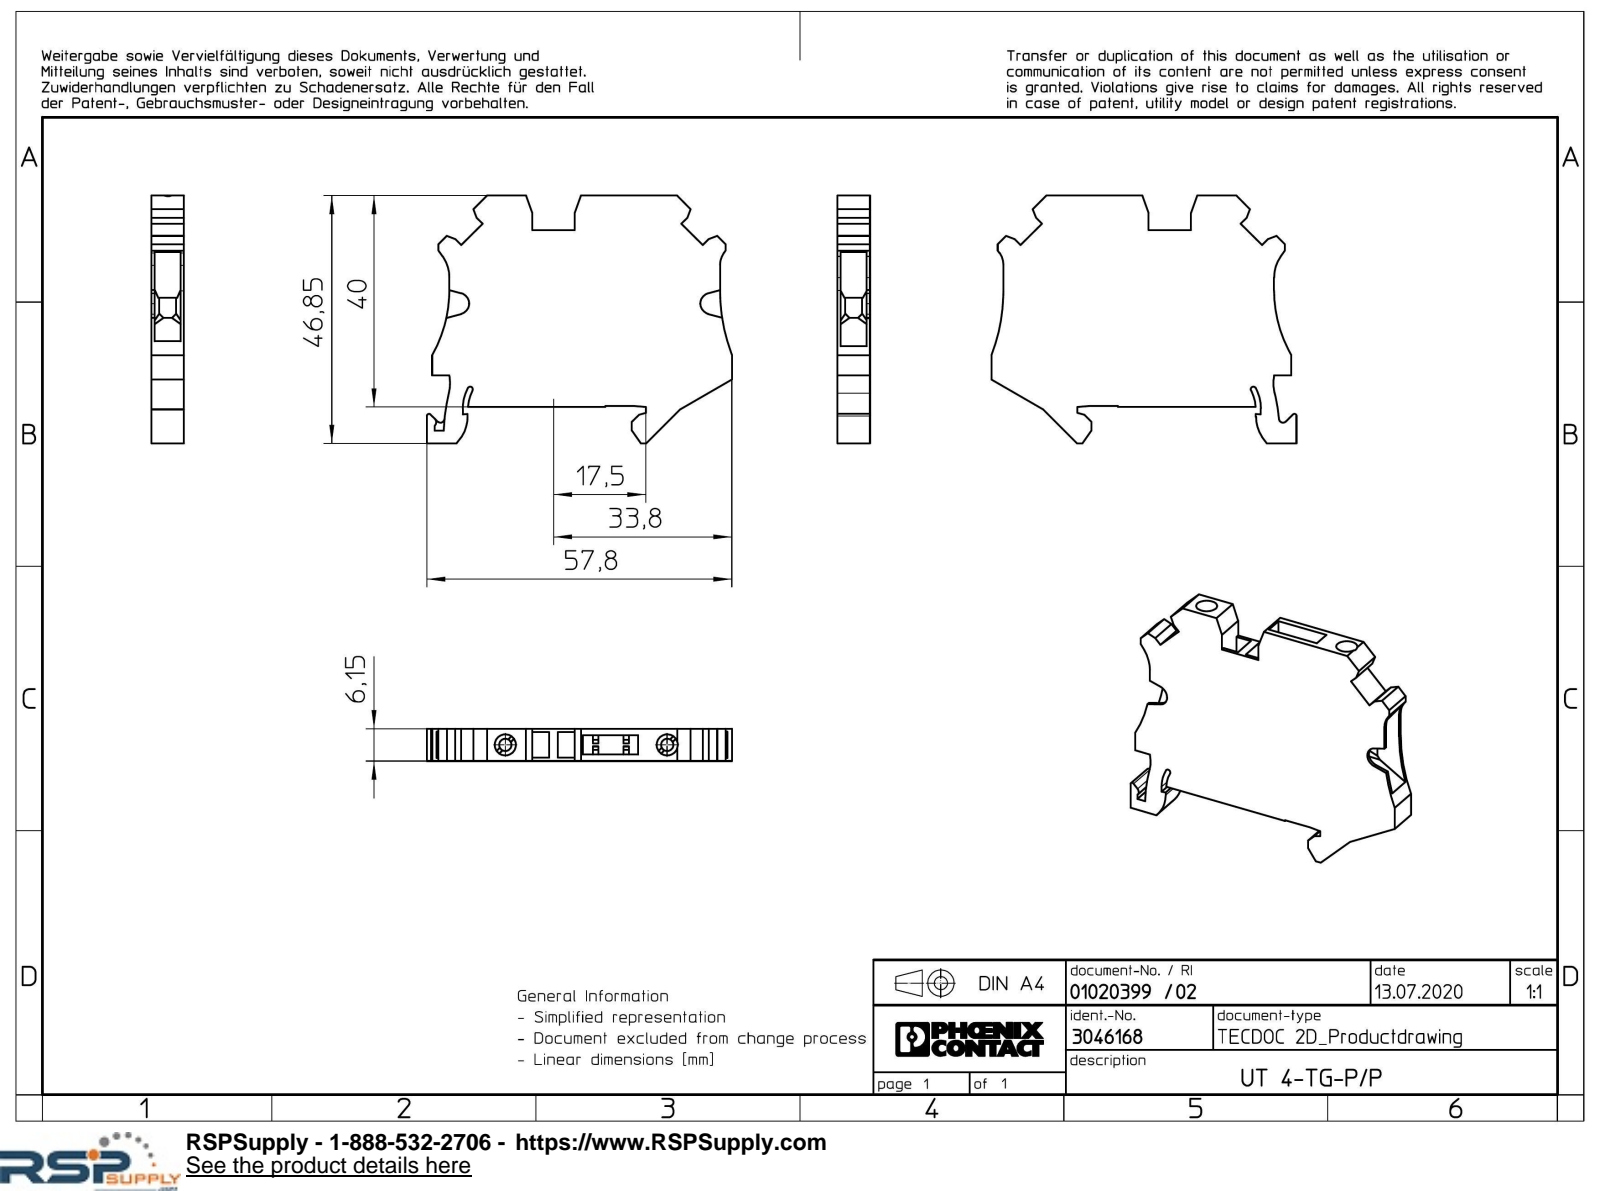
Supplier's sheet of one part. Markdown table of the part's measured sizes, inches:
| quantity | value |
| --- | --- |
| part name | UT_4-TG-P_P-select |
| STEP written by | Creo Elements/Direct Modeling 20.1A 29-Sep-2018 (C) Parametric Technology GmbH (AUTOMOTIVE_DESIGN) |
| units | inches |
| bodies | 1 solid, 190 faces (154 planar, 32 cylindrical, 4 other) |
| overall size | 2.276 × 1.844 × 0.242 |
| volume | 0.653 in³ |
| surface area | 10.62 in² |
| round holes (diameter × count) | 0.093 × 2, 0.157 × 2 |
| partial cylindrical surfaces (radius × count) | 0.079 × 4, 0.01 × 2, 0.276 × 2, 0.016 × 1, 0.02 × 1, 0.03 × 1, 0.035 × 1, 0.157 × 1 |
| main face-to-face distances | 0.242, 0.024, 0.193, 0.026, 0.219, 0.191, 0.049, 0.169, 0.217, 0.167 |
| hole center spacings | 1.207 |
